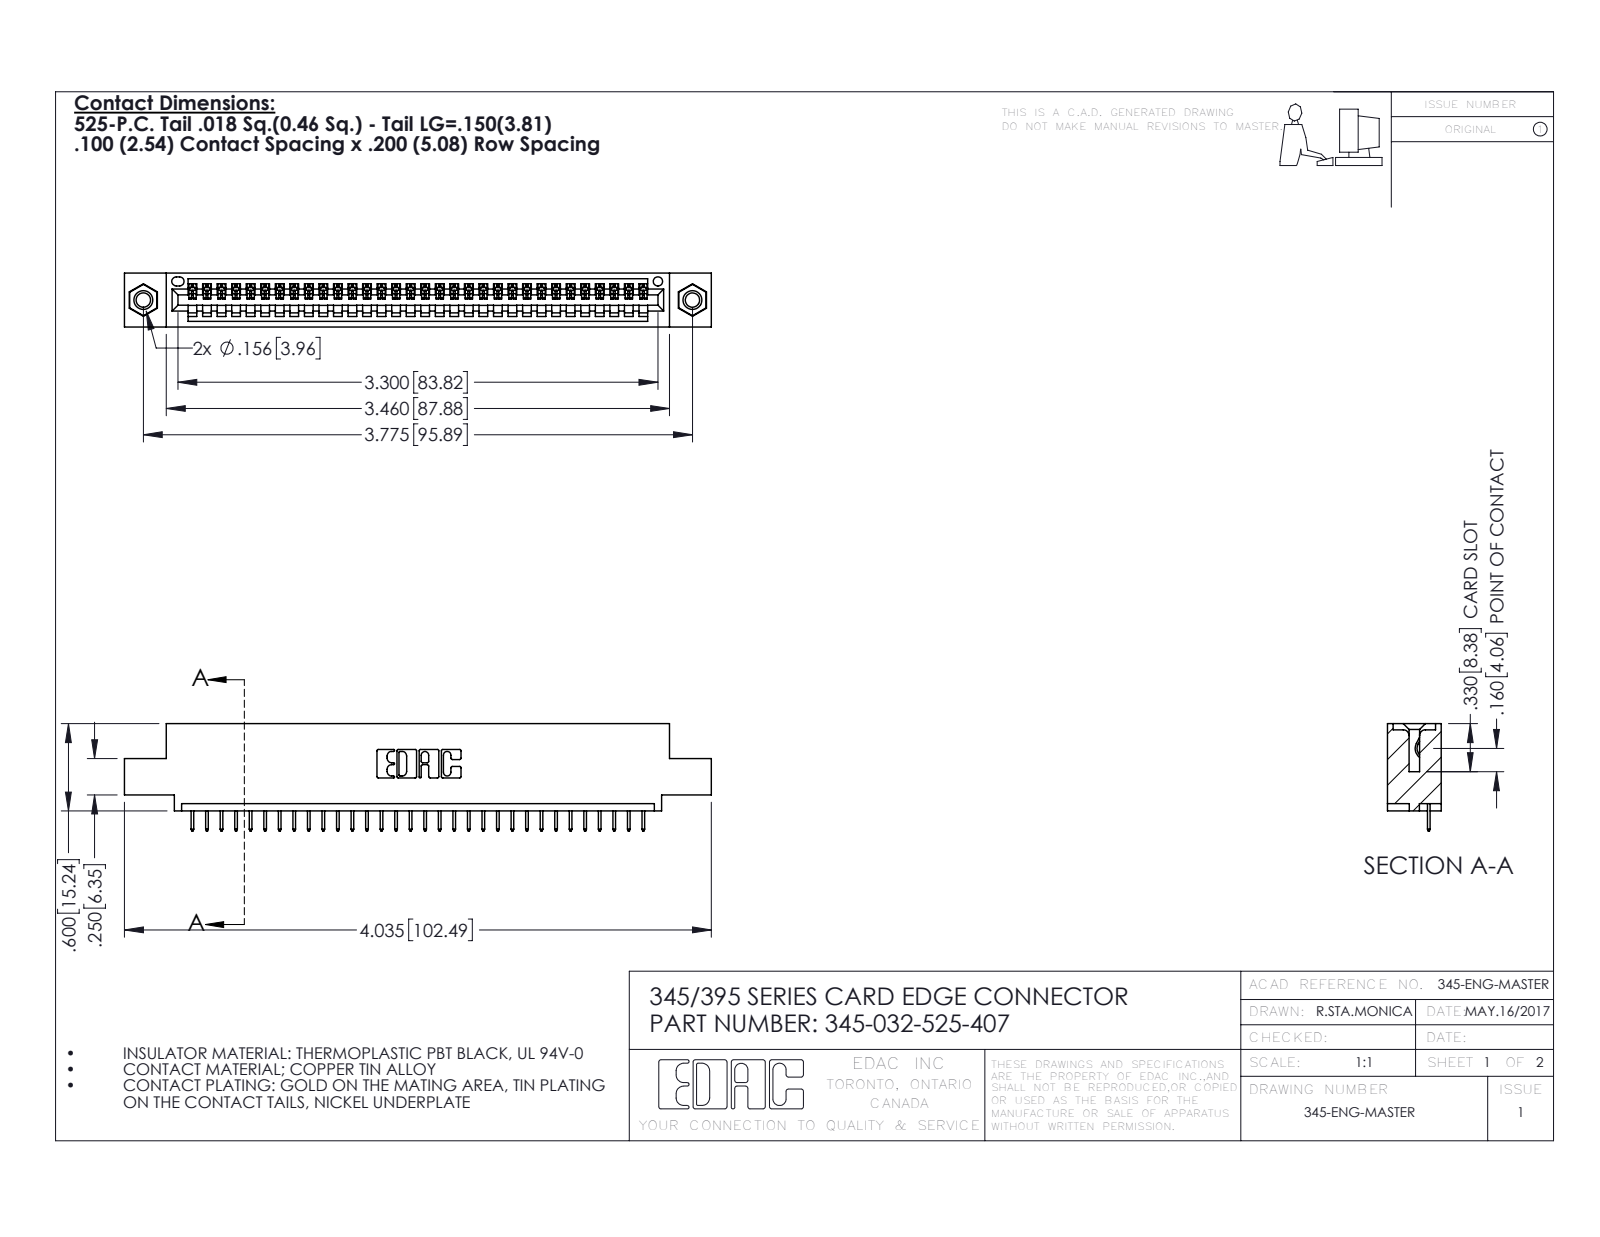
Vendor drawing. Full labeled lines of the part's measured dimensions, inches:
Part name (STEP PRODUCT): 345-292-001_345-293-125; 345-250-001_345-250-005-103; 345 Part_0.110 Offset - 0.156 Dia-TI; 345-032-525-407
STEP written by: SolidWorks 2020 (CONFIG_CONTROL_DESIGN)
Units: inches
Bodies: 35 solids, 2174 faces (1588 planar, 570 cylindrical, 16 other)
Overall size (bounding box): 4.035 × 0.737 × 0.37
Volume: 0.576 in³ · Surface area: 18.73 in²
Round holes (diameter × count): ⌀0.098 ×2, ⌀0.125 ×2, ⌀0.156 ×2, ⌀0.064 ×1
Round bosses / shafts (diameter × count): ⌀0.155 ×2
Partial cylindrical surfaces — rounded edges, fillets, slot ends (radius × count): R0.006 ×64, R0.01 ×22, R0.007 ×6, R0.031 ×6, R0.026 ×3, R0.031 ×2, R0.04 ×2, R0.014 ×1
Main face-to-face distances: 0.072, 0.298, 0.37, 0.2, 0.098, 0.272, 0.025, 0.225, 0.072, 0.149
Hole centre spacings: 0.27, 3.54, 3.775
